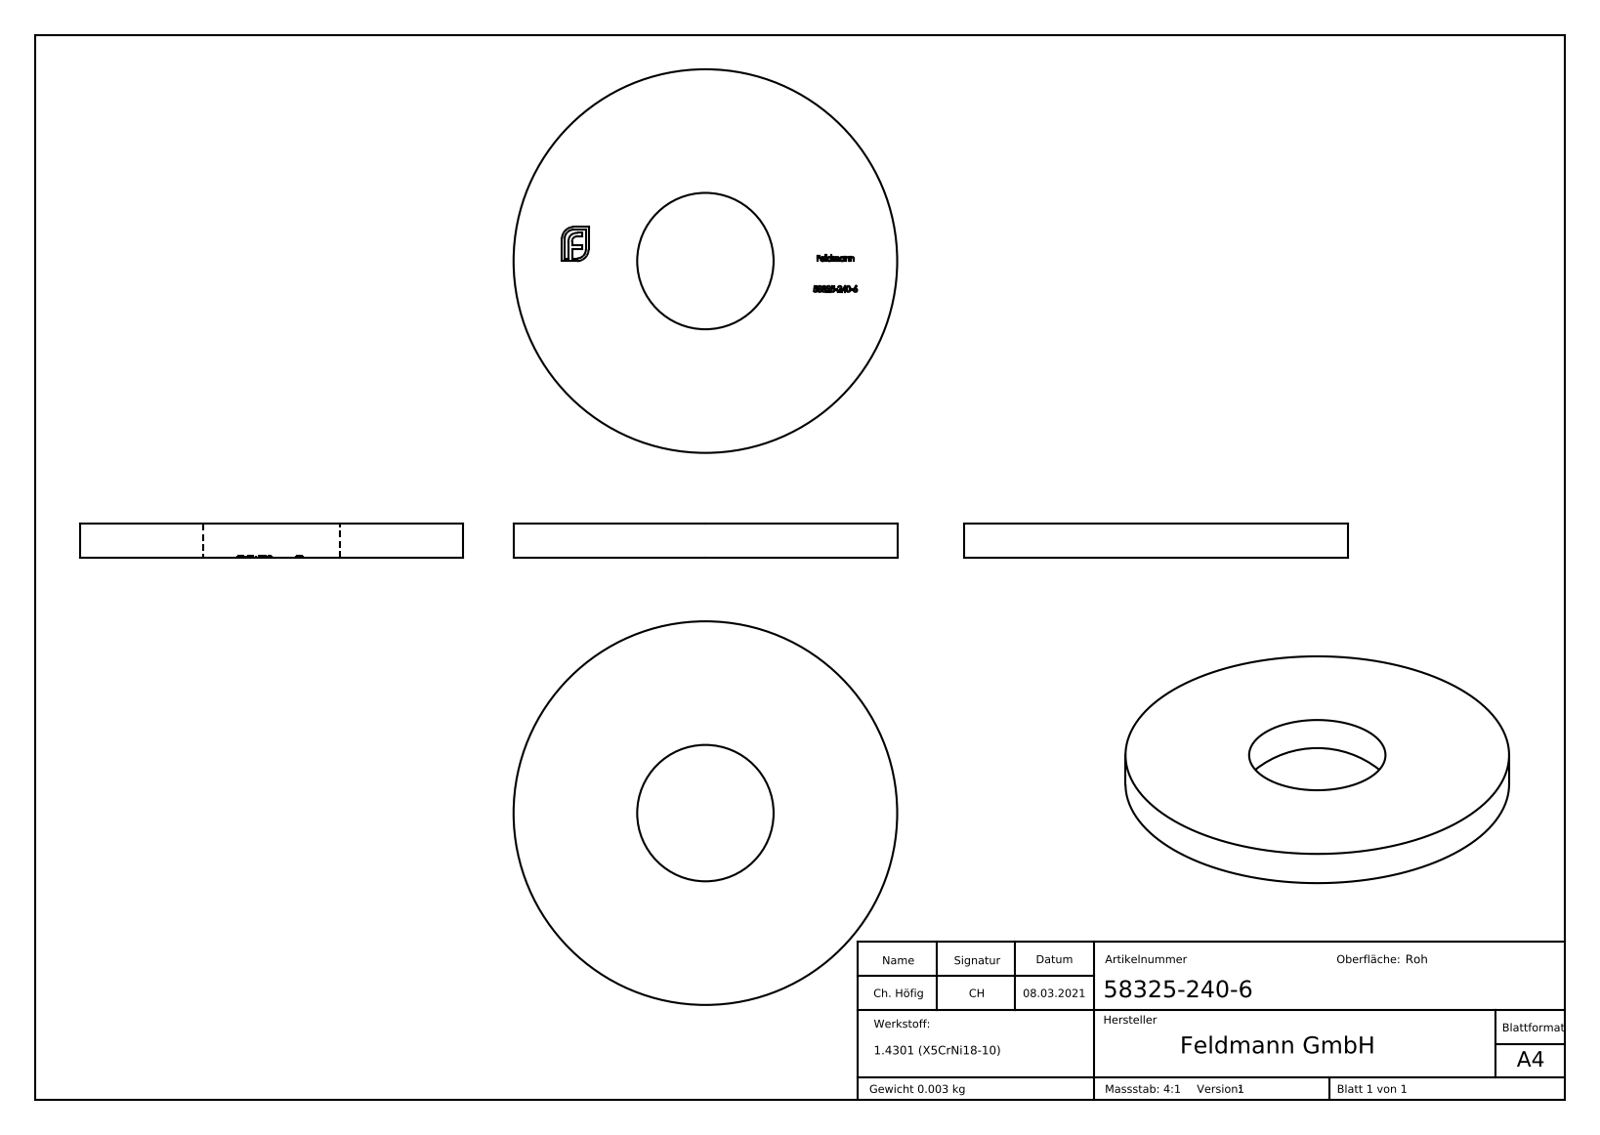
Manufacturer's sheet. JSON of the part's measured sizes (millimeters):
{"part_name": "58325-240-6", "step_written_by": "SolidWorks 2018 (CONFIG_CONTROL_DESIGN)", "units": "millimeters", "bodies": {"solids": 1, "faces": 304, "planar": 155, "cylindrical": 4, "other": 145}, "overall_size": [18, 18, 1.6], "volume_mm3": 356, "surface_area_mm2": 571, "round_holes": [[6.4, 1]], "round_bosses_or_shafts": [[18, 1]], "face_to_face_distances": [1.6, 1.5, 1.12, 0.65, 1.47, 1.25, 0.89, 0.58, 0.99, 1.44]}
